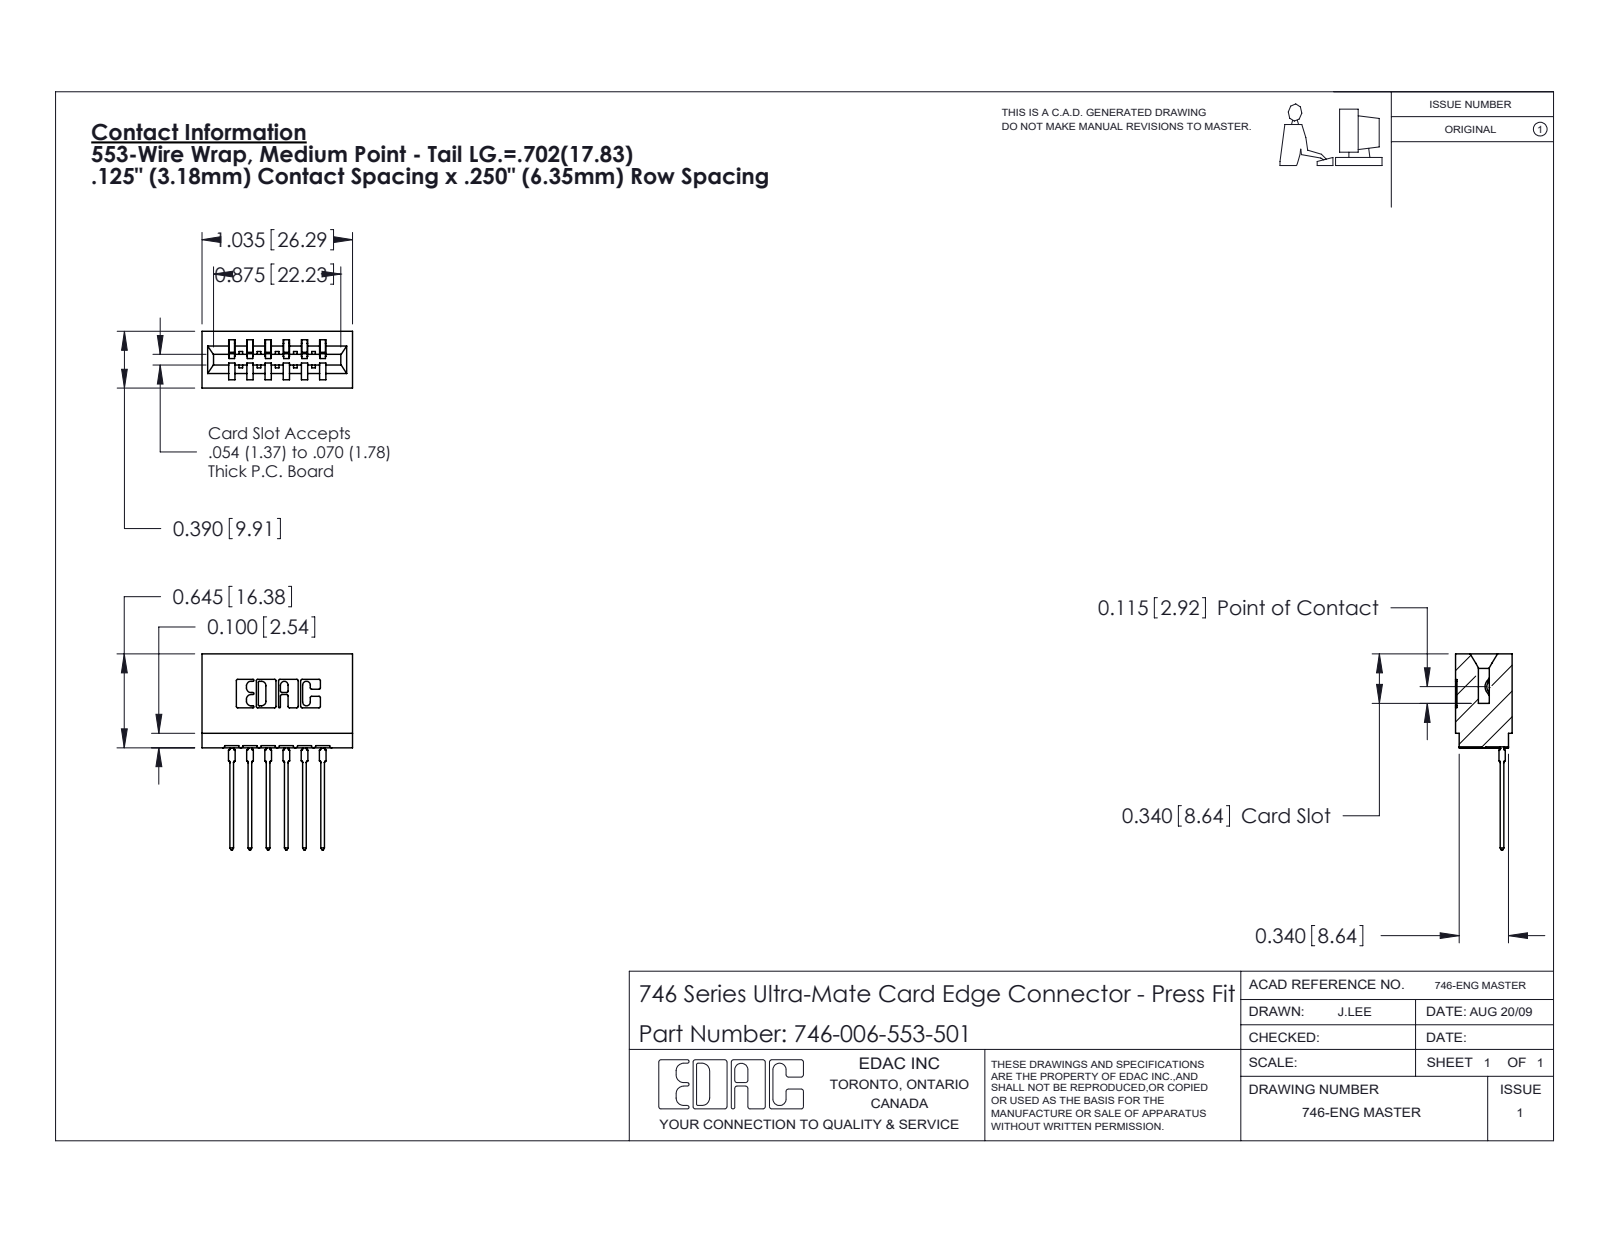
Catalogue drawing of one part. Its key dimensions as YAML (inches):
part_name: "746-006-553-501; 746 Part_.340 Slot Depth - 01; 746-292-001_553"
step_written_by: "SolidWorks 2020 (CONFIG_CONTROL_DESIGN)"
units: inches
bodies: {solids: 7, faces: 745, planar: 433, cylindrical: 156, other: 156}
overall_size: [1.346, 1.035, 0.39]
volume: 0.195
surface_area: 6.001
partial_cylinders:
  - {radius: 0.01, count: 22}
  - {radius: 0.021, count: 12}
  - {radius: 0.015, count: 7}
  - {radius: 0.007, count: 6}
  - {radius: 0.031, count: 6}
  - {radius: 0.005, count: 4}
  - {radius: 0.011, count: 4}
  - {radius: 0.026, count: 3}
face_to_face_distances: [0.25, 0.125, 0.042, 0.333, 0.057, 0.375, 0.39, 0.292, 0.5, 0.208]
